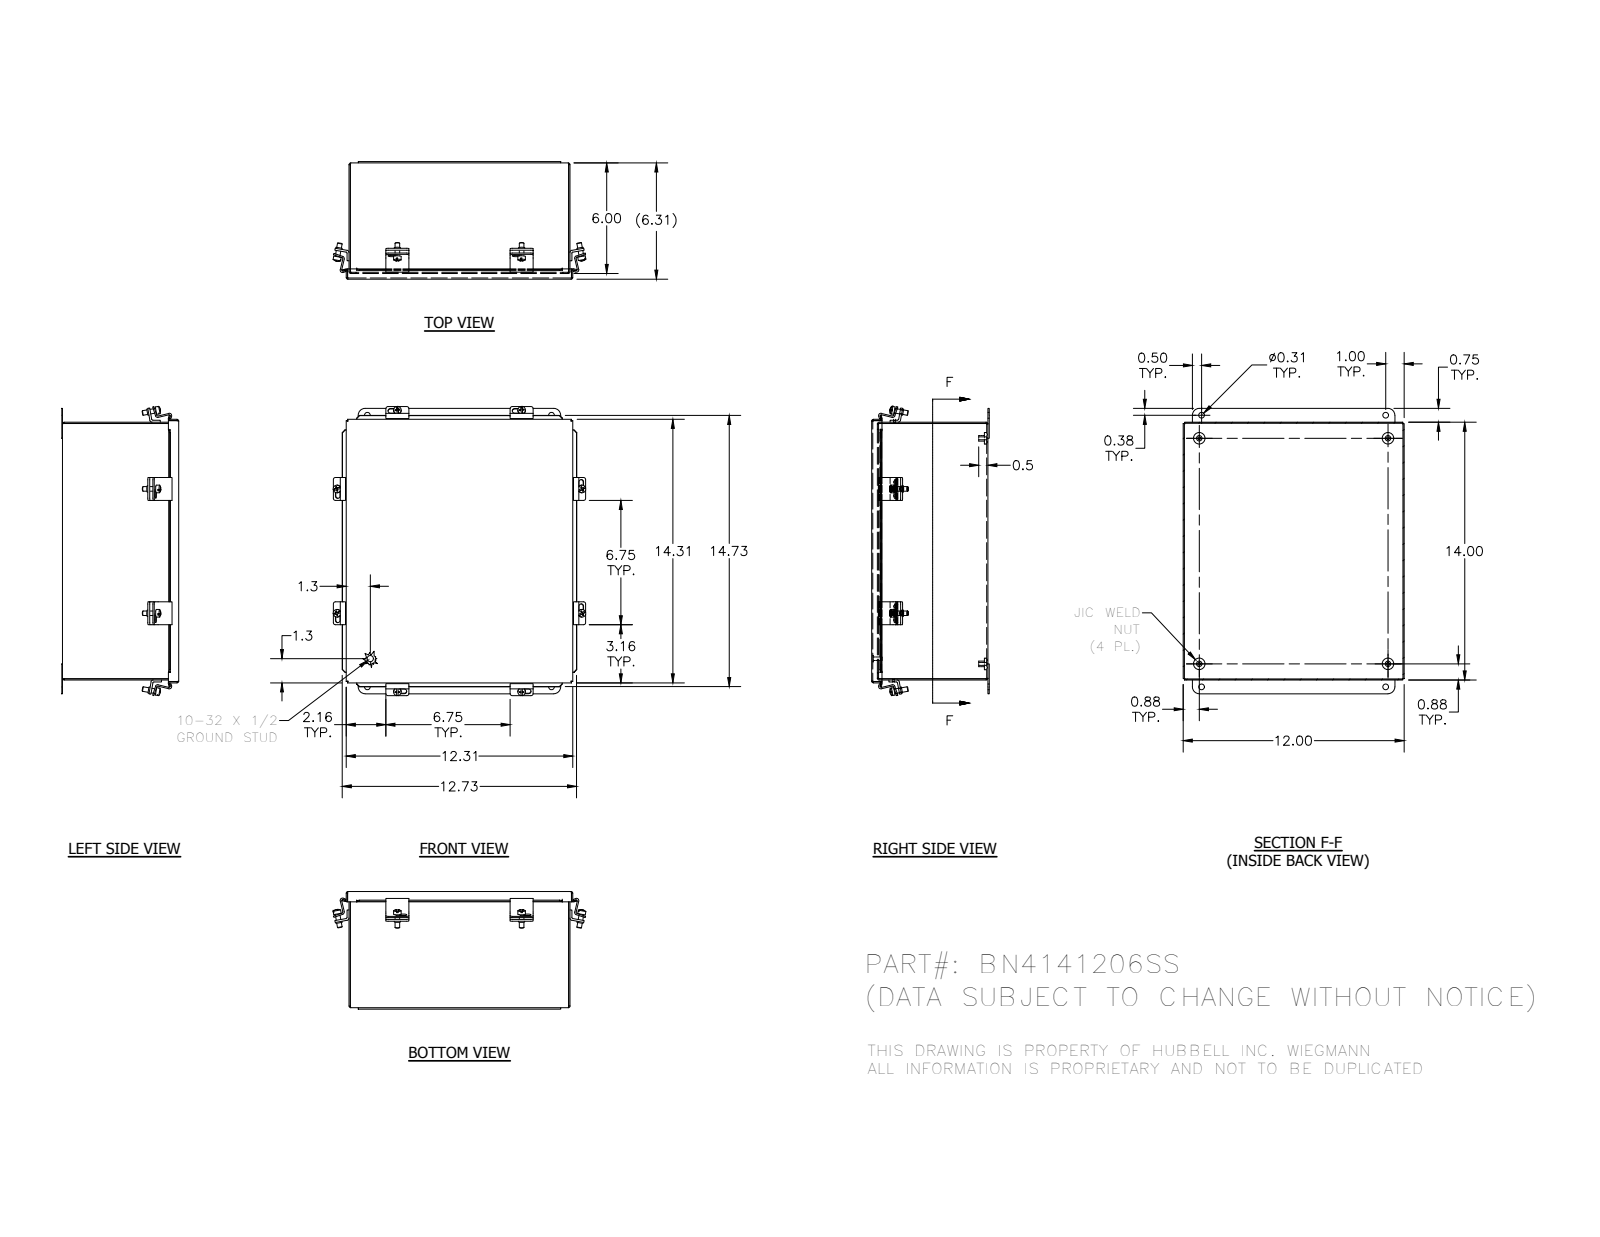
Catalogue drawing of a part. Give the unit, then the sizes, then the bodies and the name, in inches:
Units: inches
Overall size (bounding box): 15.712 × 13.724 × 6.388
Round holes (diameter × count): ⌀0.11 ×12, ⌀0.196 ×8, ⌀0.156 ×4, ⌀0.31 ×4
Round bosses / shafts (diameter × count): ⌀0.41 ×8, ⌀0.344 ×8, ⌀0.25 ×8, ⌀0.625 ×4, ⌀0.3 ×4, ⌀0.337 ×1, ⌀0.19 ×1
Partial cylindrical surfaces — rounded edges, fillets, slot ends (radius × count): R0.125 ×32, R0.031 ×16, R0.094 ×16, R0.133 ×16, R0.063 ×12, R0.126 ×12, R0.375 ×4
Main face-to-face distances: 0.063, 6.25, 6.313, 6.187, 11.937, 13.937, 12, 11.875, 14, 13.875
Hole centre spacings: 6.75, 0.75, 0.063, 0.753, 1.256, 6.75, 13.5, 6
Volume: 49.23 in³ · Surface area: 1 554 in²
Bodies: 33 solids, 917 faces (439 planar, 328 cylindrical, 150 other)
Part name (STEP PRODUCT): BN41412SSLID_1; 34856_1; C2002_1; C2001_1 (+5 more)
STEP written by: SolidWorks 2014 (AUTOMOTIVE_DESIGN)
